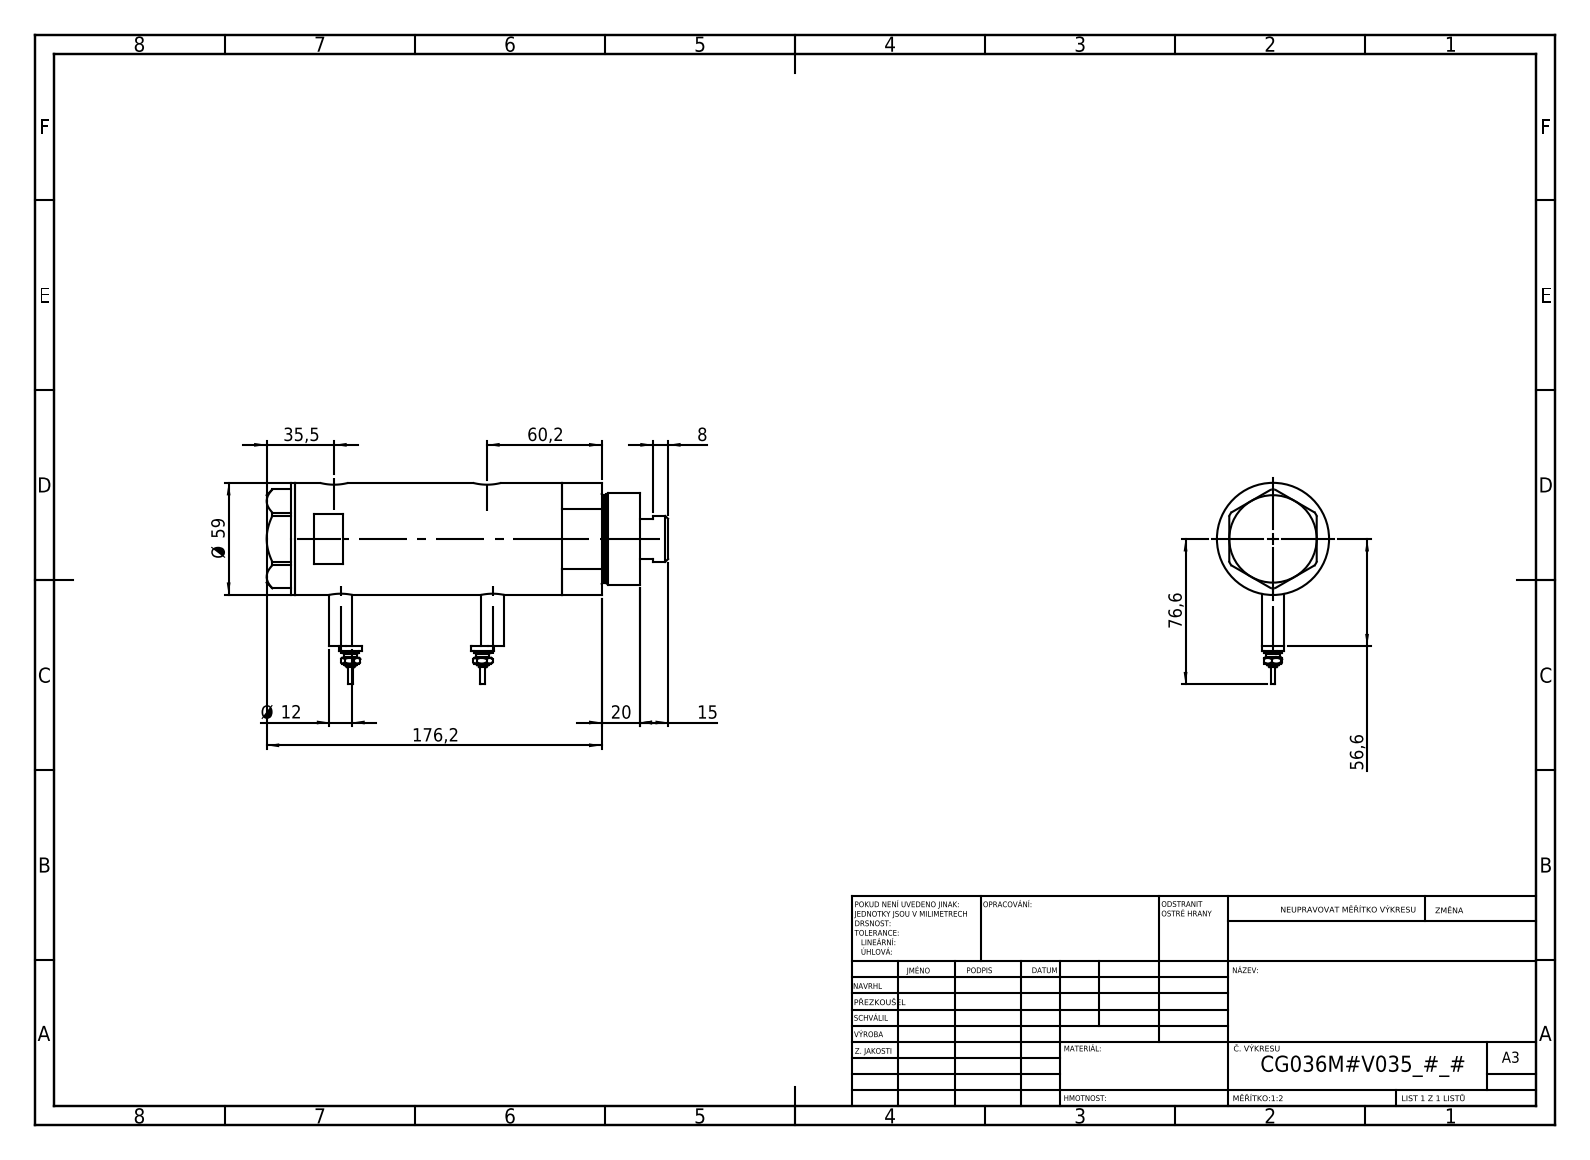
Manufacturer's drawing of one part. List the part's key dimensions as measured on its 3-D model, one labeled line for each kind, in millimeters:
Part name (STEP PRODUCT): V270CG_FRONT; Switch; V270CG_MIDDLE; V270CG_VC (+1 more)
STEP written by: SolidWorks 2019 (CONFIG_CONTROL_DESIGN)
Units: millimetres
Bodies: 6 solids, 212 faces (79 planar, 69 cylindrical, 64 other)
Overall size (bounding box): 211.2 × 106.1 × 59
Volume: 492 363 mm³ · Surface area: 103 272 mm²
Round holes (diameter × count): ⌀9.73 ×2, ⌀12.5 ×2, ⌀15 ×2, ⌀8.5 ×1, ⌀25 ×1, ⌀26.5 ×1, ⌀36 ×1, ⌀40 ×1, ⌀52 ×1
Round bosses / shafts (diameter × count): ⌀12 ×4, ⌀9 ×2, ⌀7 ×2, ⌀4.5 ×2, ⌀2.5 ×2, ⌀59 ×1, ⌀48 ×1, ⌀46 ×1
Main face-to-face distances: 102.2, 23.5, 78.7, 15, 38.5, 117.2, 2, 196.2, 181.2, 157.7
Hole centre spacings: 2.9, 3.5, 77, 79.9, 80.5, 83.4
